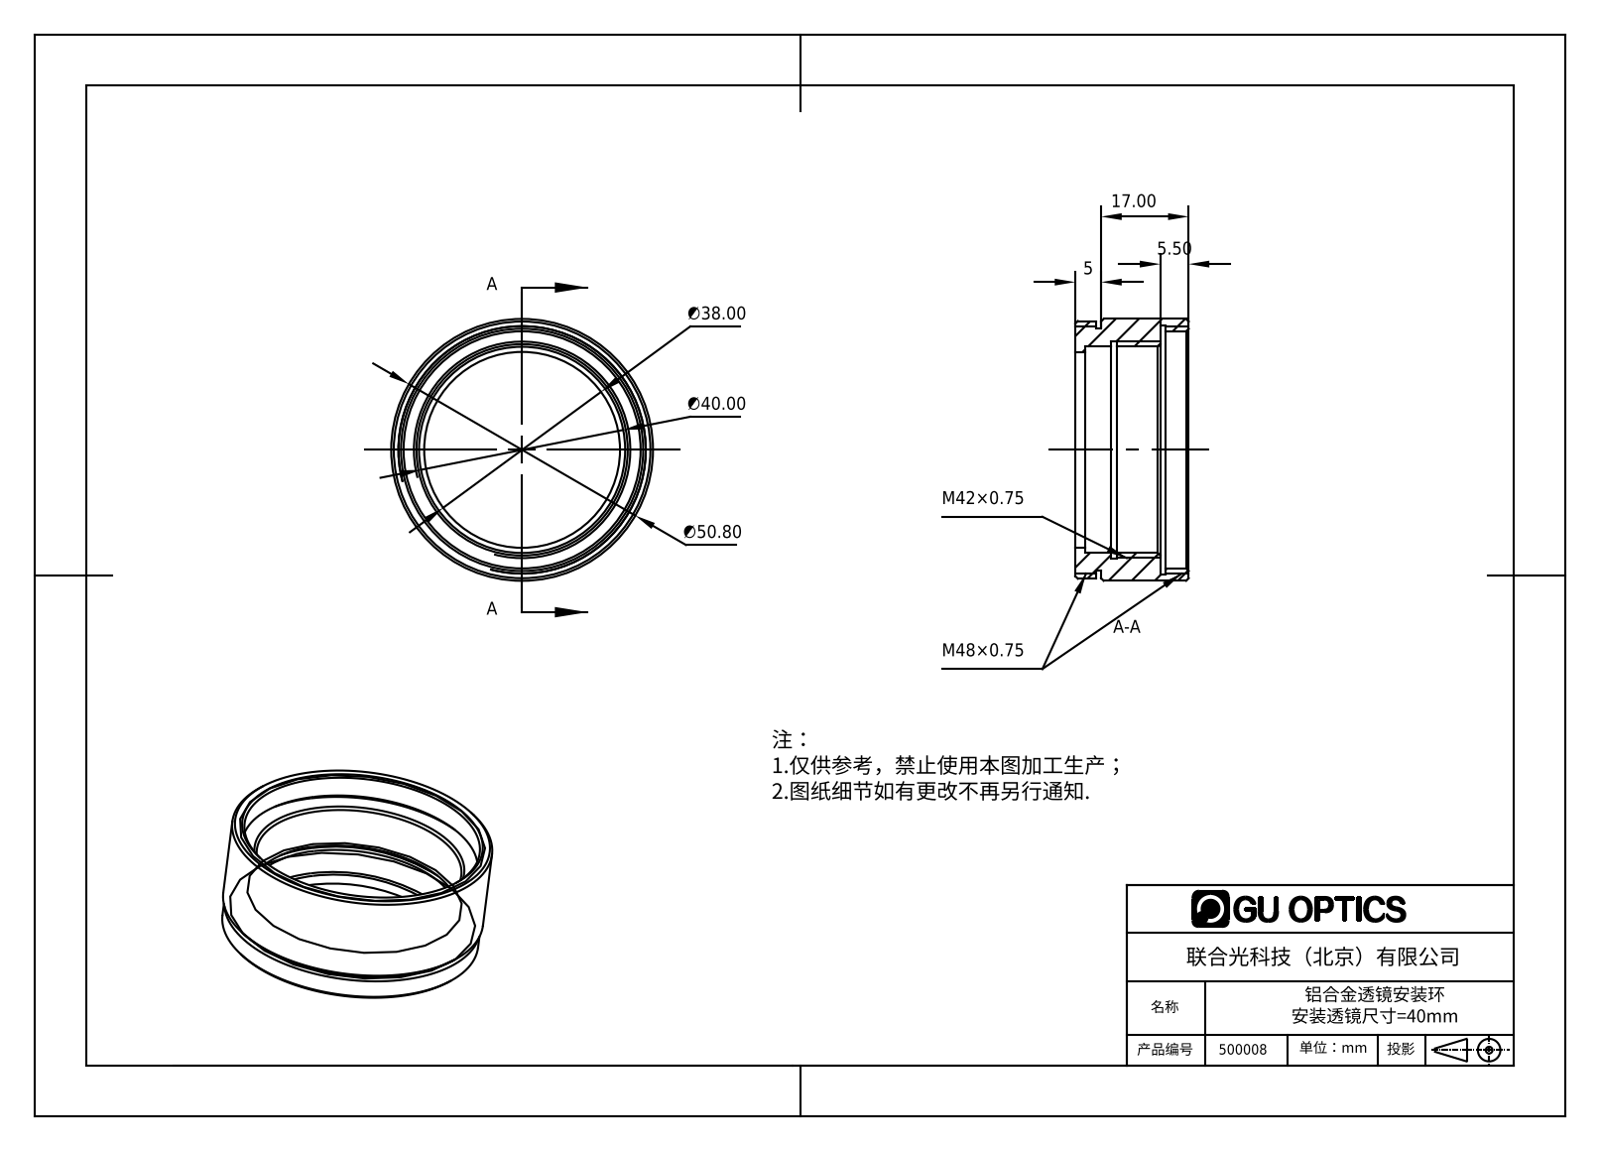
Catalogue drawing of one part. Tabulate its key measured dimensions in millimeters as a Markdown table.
| quantity | value |
| --- | --- |
| part name | 500008 |
| STEP written by | SolidWorks 2016 (AUTOMOTIVE_DESIGN) |
| units | millimeters |
| bodies | 1 solid, 37 faces (9 planar, 18 cylindrical, 10 other) |
| overall size | 50.8 × 50.8 × 22 |
| volume | 14 003 mm³ |
| surface area | 9 021 mm² |
| round holes (diameter × count) | 38 × 1, 40 × 1, 42.3 × 1, 46 × 1, 48.3 × 1 |
| round bosses / shafts (diameter × count) | 50.8 × 1, 50 × 1, 47 × 1 |
| main face-to-face distances | 1, 16.5, 3, 12.5, 2, 4, 5, 9.5, 11.5, 22 |
